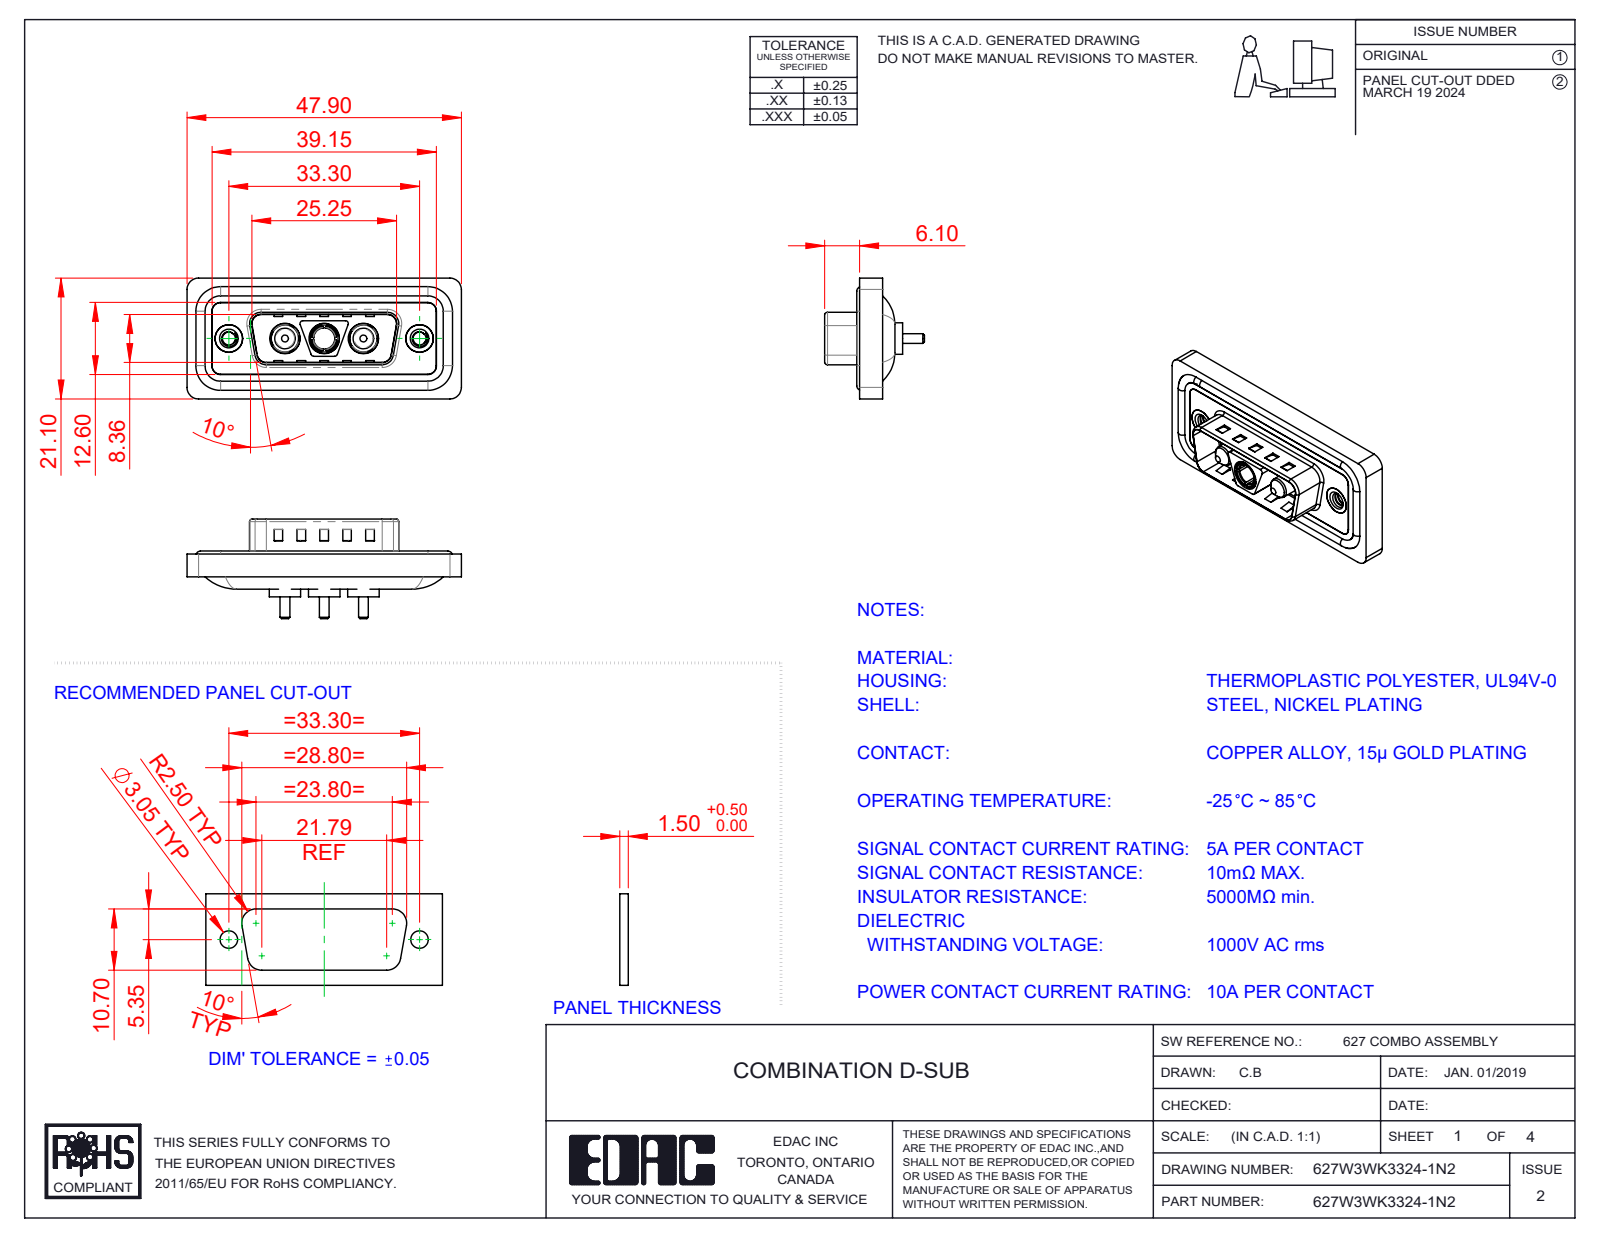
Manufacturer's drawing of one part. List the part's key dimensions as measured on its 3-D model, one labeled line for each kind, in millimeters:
Part name (STEP PRODUCT): 627Combo Shell Rear_15 Contacts; 627Combo Shell Front_15 Contacts; 627W3WK3324-1N2; Power Pin_10A S (+4 more)
STEP written by: SolidWorks 2023 (CONFIG_CONTROL_DESIGN)
Units: millimetres
Bodies: 13 solids, 609 faces (231 planar, 250 cylindrical, 128 other)
Overall size (bounding box): 47.9 × 21.1 × 17.4
Volume: 5 644 mm³ · Surface area: 9 089 mm²
Round holes (diameter × count): ⌀4.85 ×3, ⌀5.3 ×3, ⌀2.26 ×2, ⌀4 ×2, ⌀4.8 ×2, ⌀5 ×2, ⌀3.7 ×1
Round bosses / shafts (diameter × count): ⌀1.6 ×4, ⌀5.5 ×3, ⌀5.2 ×3, ⌀4.75 ×3, ⌀3.75 ×3, ⌀1.7 ×3, ⌀4.9 ×2, ⌀3.6 ×2
Partial cylindrical surfaces — rounded edges, fillets, slot ends (radius × count): R1.5 ×26, R2 ×20, R0.5 ×12, R1.6 ×8, R0.25 ×4, R0.6 ×4, R0.65 ×4, R0.9 ×4
Main face-to-face distances: 0.4, 1.5, 1.1, 0.5, 1.6, 3.1, 2.9, 4, 0.82, 9.58
Hole centre spacings: 6.85, 9.8, 16.65, 23.5, 13.7, 33.3
